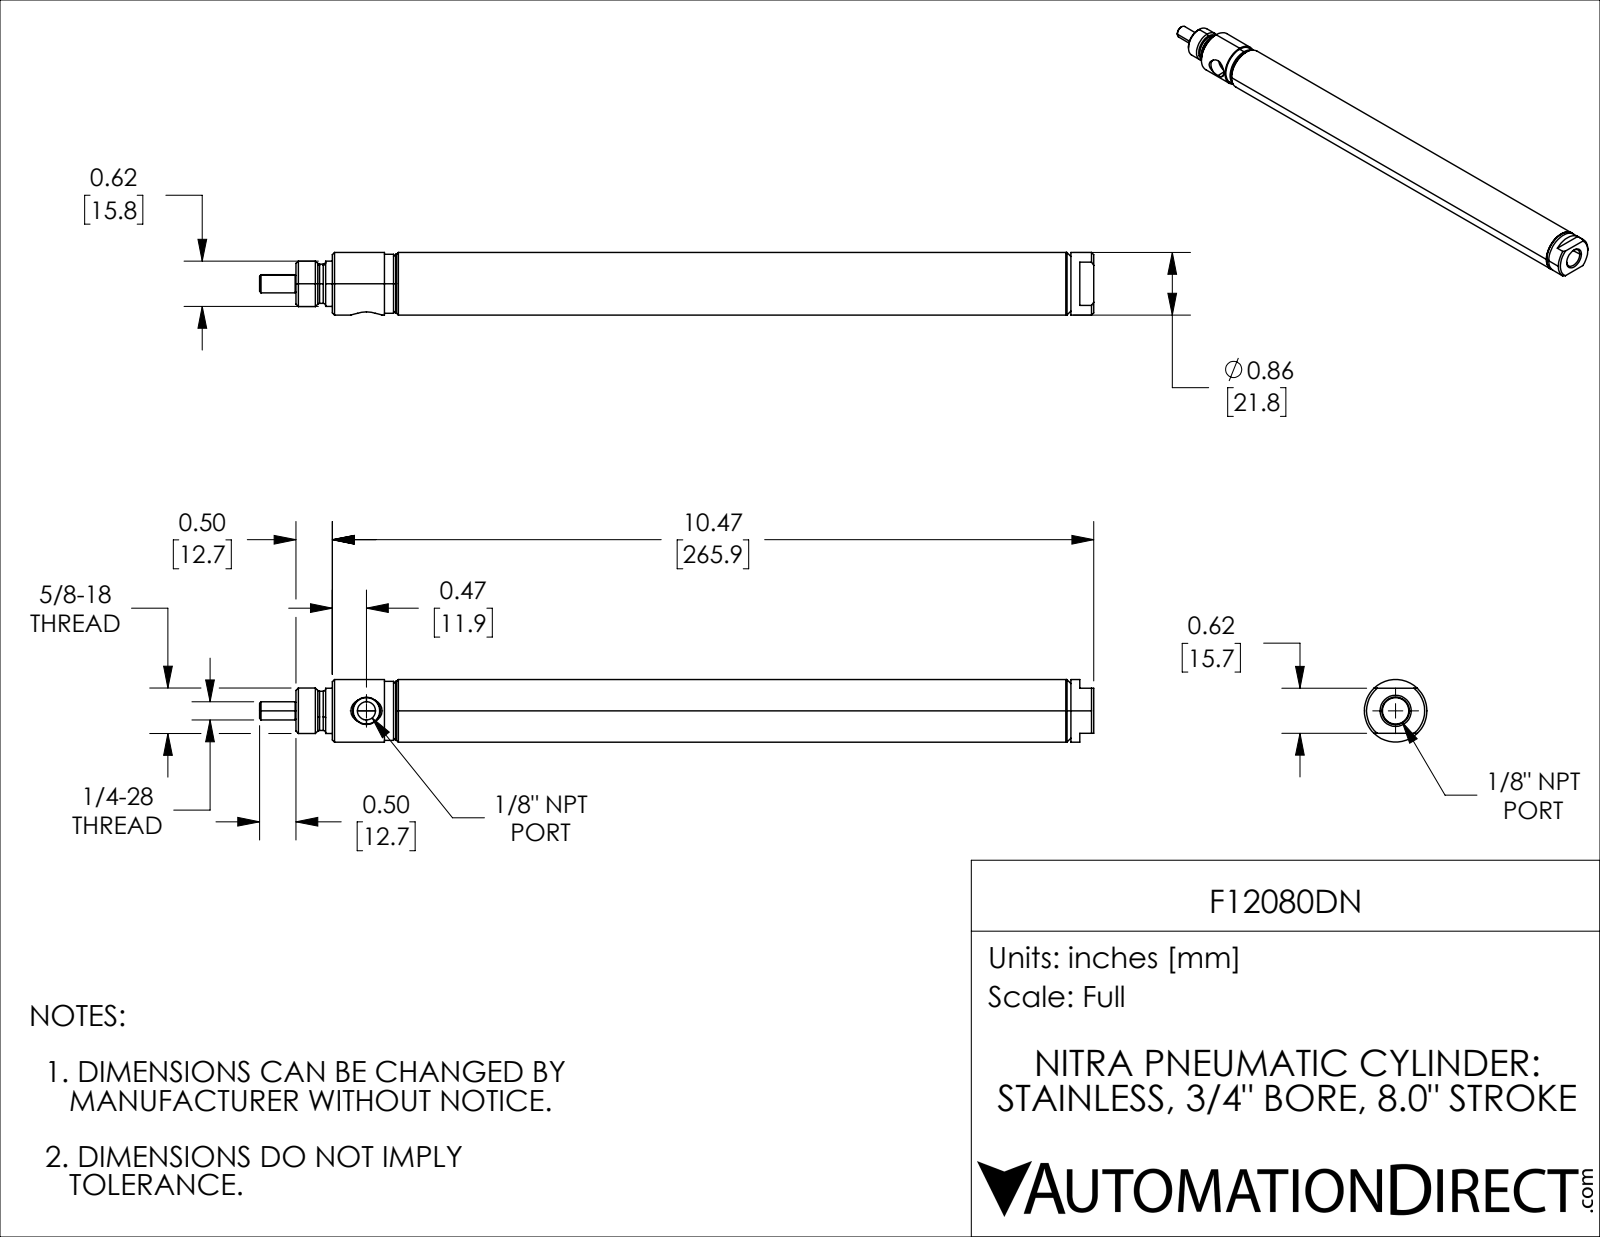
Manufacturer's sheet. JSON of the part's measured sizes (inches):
{"part_name": "F12080DN_5; F12080DN; F12080DN_7; F12080DN_3 (+1 more)", "step_written_by": "SolidWorks 2021 (CONFIG_CONTROL_DESIGN)", "units": "inches", "bodies": {"solids": 4, "faces": 124, "planar": 22, "cylindrical": 46, "other": 56}, "overall_size": [11.469, 0.86, 0.86], "volume_in3": 2.828, "surface_area_in2": 68.63, "round_holes": [[0.25, 1], [0.274, 1], [0.5, 1], [0.702, 1]], "round_bosses_or_shafts": [[0.86, 1], [0.81, 1], [0.762, 1], [0.625, 1], [0.622, 1], [0.539, 1], [0.25, 1], [0.23, 1]], "face_to_face_distances": [0.844, 8, 8.844, 9.375, 1.375, 0.531, 0.5, 1.094, 9.094, 9.938]}
